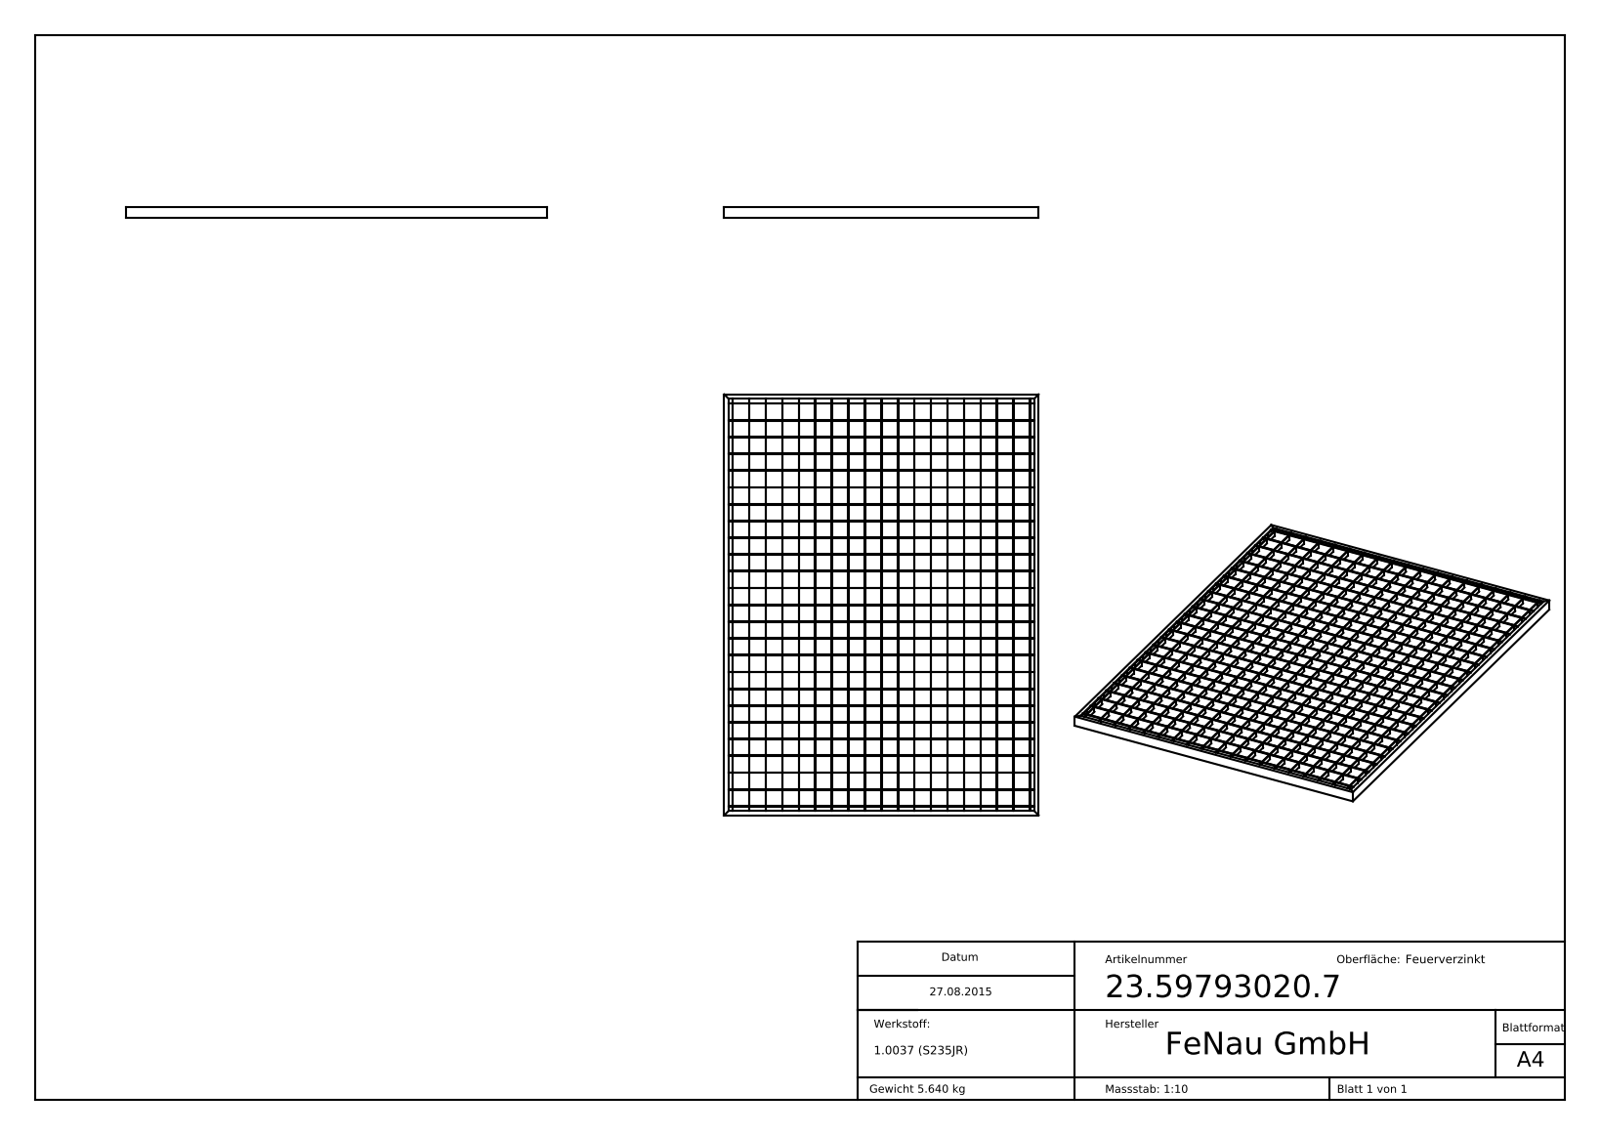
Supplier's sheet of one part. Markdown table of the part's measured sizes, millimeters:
| quantity | value |
| --- | --- |
| part name | 23-59793020-7 |
| STEP written by | SolidWorks 2015 (CONFIG_CONTROL_DESIGN) |
| units | millimeters |
| bodies | 1 solid, 1778 faces (1778 planar, 0 cylindrical, 0 other) |
| overall size | 790 × 590 × 20 |
| volume | 723 079 mm³ |
| surface area | 1 082 000 mm² |
| main face-to-face distances | 63, 31.5, 94.5, 126, 157.5, 189, 220.5, 252, 283.5, 31 |
